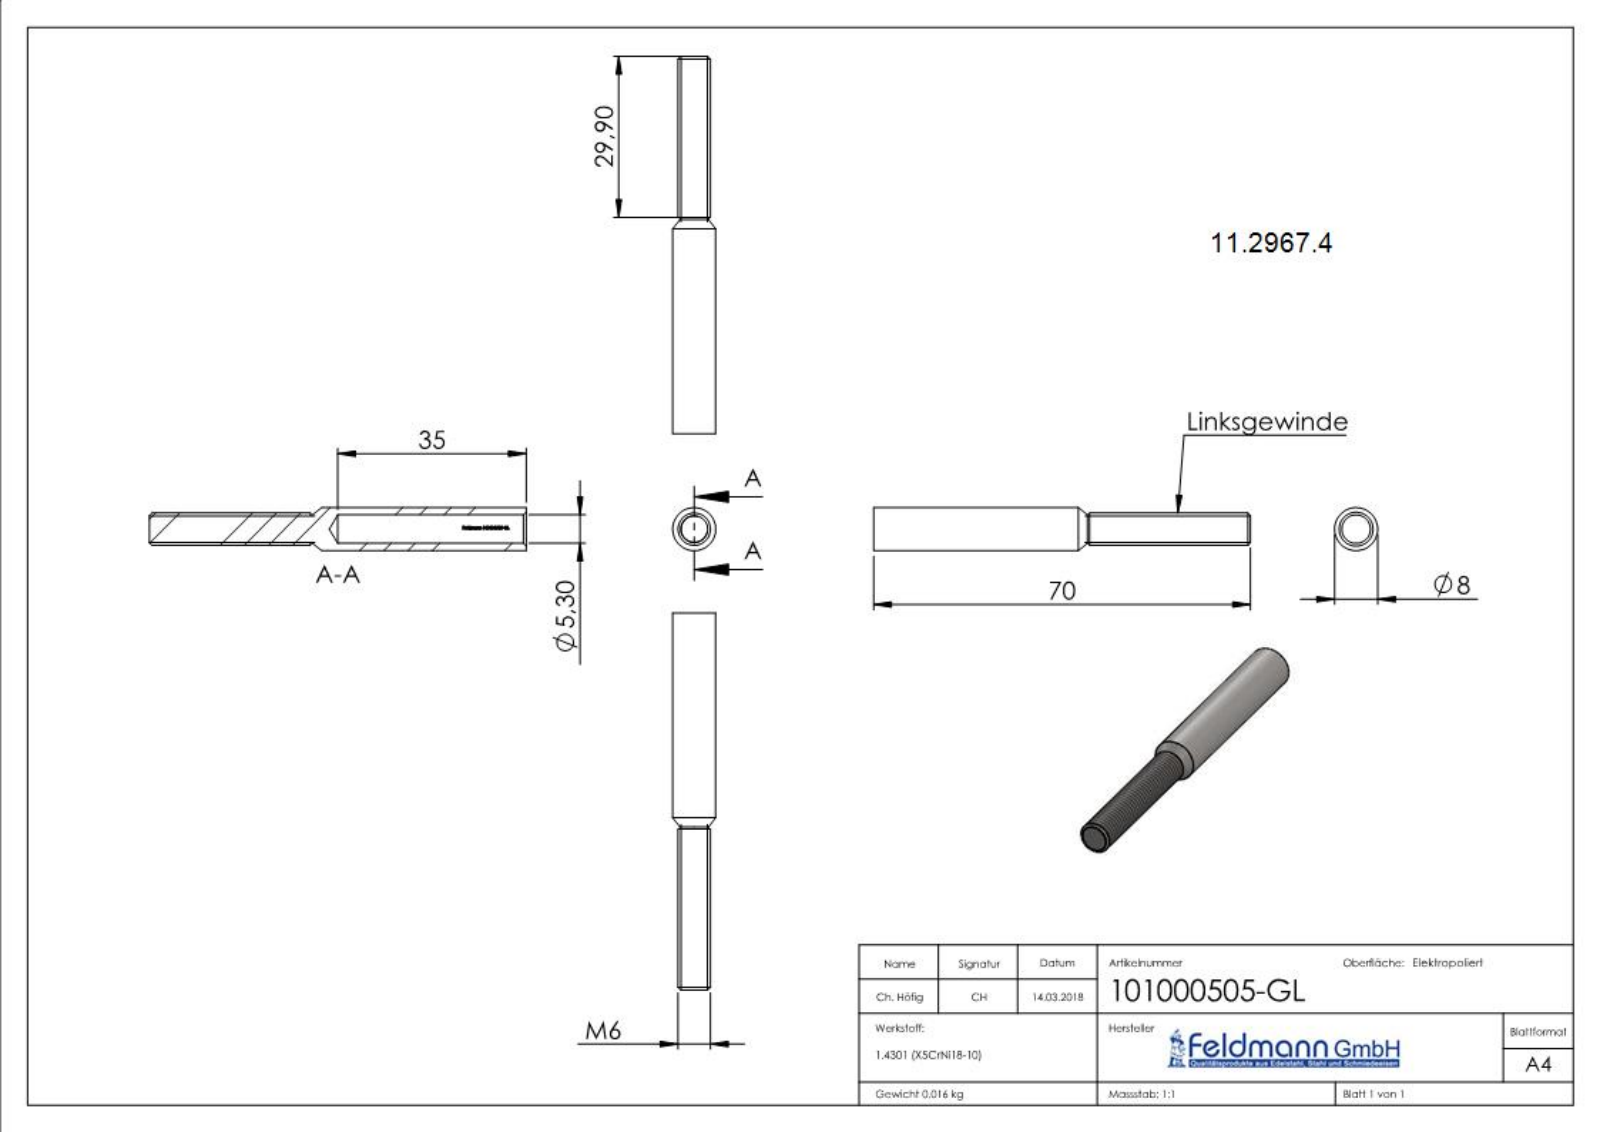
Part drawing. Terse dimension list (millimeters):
name: 101000505-GL
written by: SolidWorks 2015 (CONFIG_CONTROL_DESIGN)
unit: mm
bodies: 1 solid, 257 faces (95 planar, 36 cylindrical, 126 other)
size: 70 × 8 × 8
volume: 2 036 mm³; area: 2 236 mm²
holes: 1× ⌀5.3
bosses: 1× ⌀8, 1× ⌀6
rounds: 1× R2.75
face distances: 70, 40.1, 29.9, 7.5, 3.07, 0.82, 3.89, 4.43, 3.61, 8.31
